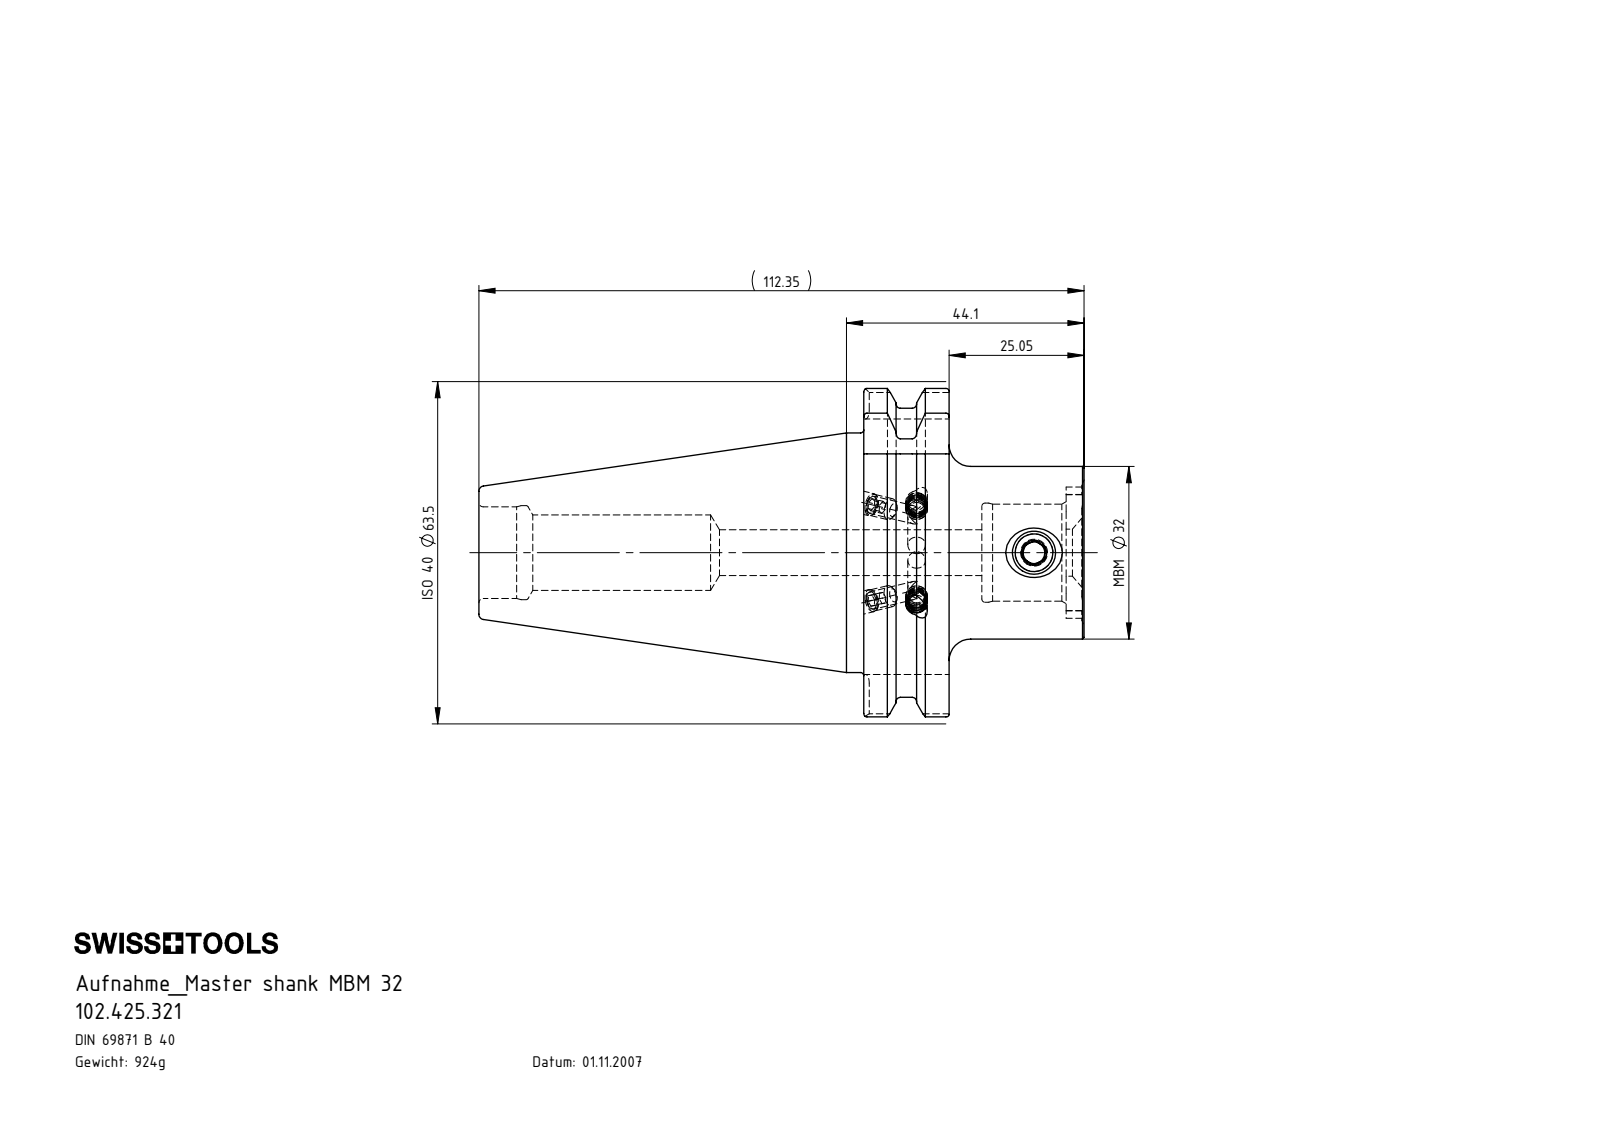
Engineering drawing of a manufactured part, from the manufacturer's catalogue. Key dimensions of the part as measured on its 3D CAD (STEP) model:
Part name (STEP PRODUCT): ISO 4026 - M4 x 5_PreviewCfg; SB4-MB3.K01.044_D_mit Bundkhlung; KVT_MB_600_040; MB3-ER1.001.011_A (+1 more)
STEP written by: SolidWorks 2017 (CONFIG_CONTROL_DESIGN)
Units: millimetres
Bodies: 8 solids, 301 faces (79 planar, 88 cylindrical, 134 other)
Overall size (bounding box): 112.35 × 63.5 × 60.94
Volume: 117 767 mm³ · Surface area: 24 649 mm²
Round holes (diameter × count): ⌀3.3 ×3, ⌀3 ×2, ⌀4 ×2, ⌀4.2 ×2, ⌀7 ×1, ⌀8.5 ×1, ⌀14 ×1, ⌀17 ×1, ⌀17.45 ×1, ⌀18 ×1, ⌀18.4 ×1
Round bosses / shafts (diameter × count): ⌀4 ×4, ⌀44.45 ×1, ⌀32 ×1, ⌀8 ×1
Partial cylindrical surfaces — rounded edges, fillets, slot ends (radius × count): R1.6 ×8, R3.2 ×4, R10.5 ×1, R12.18 ×1, R28 ×1, R31.75 ×1
Main face-to-face distances: 15.85, 47.4, 40.9, 25.05, 21.9, 6.05, 19, 37.55, 21.7, 15.65
